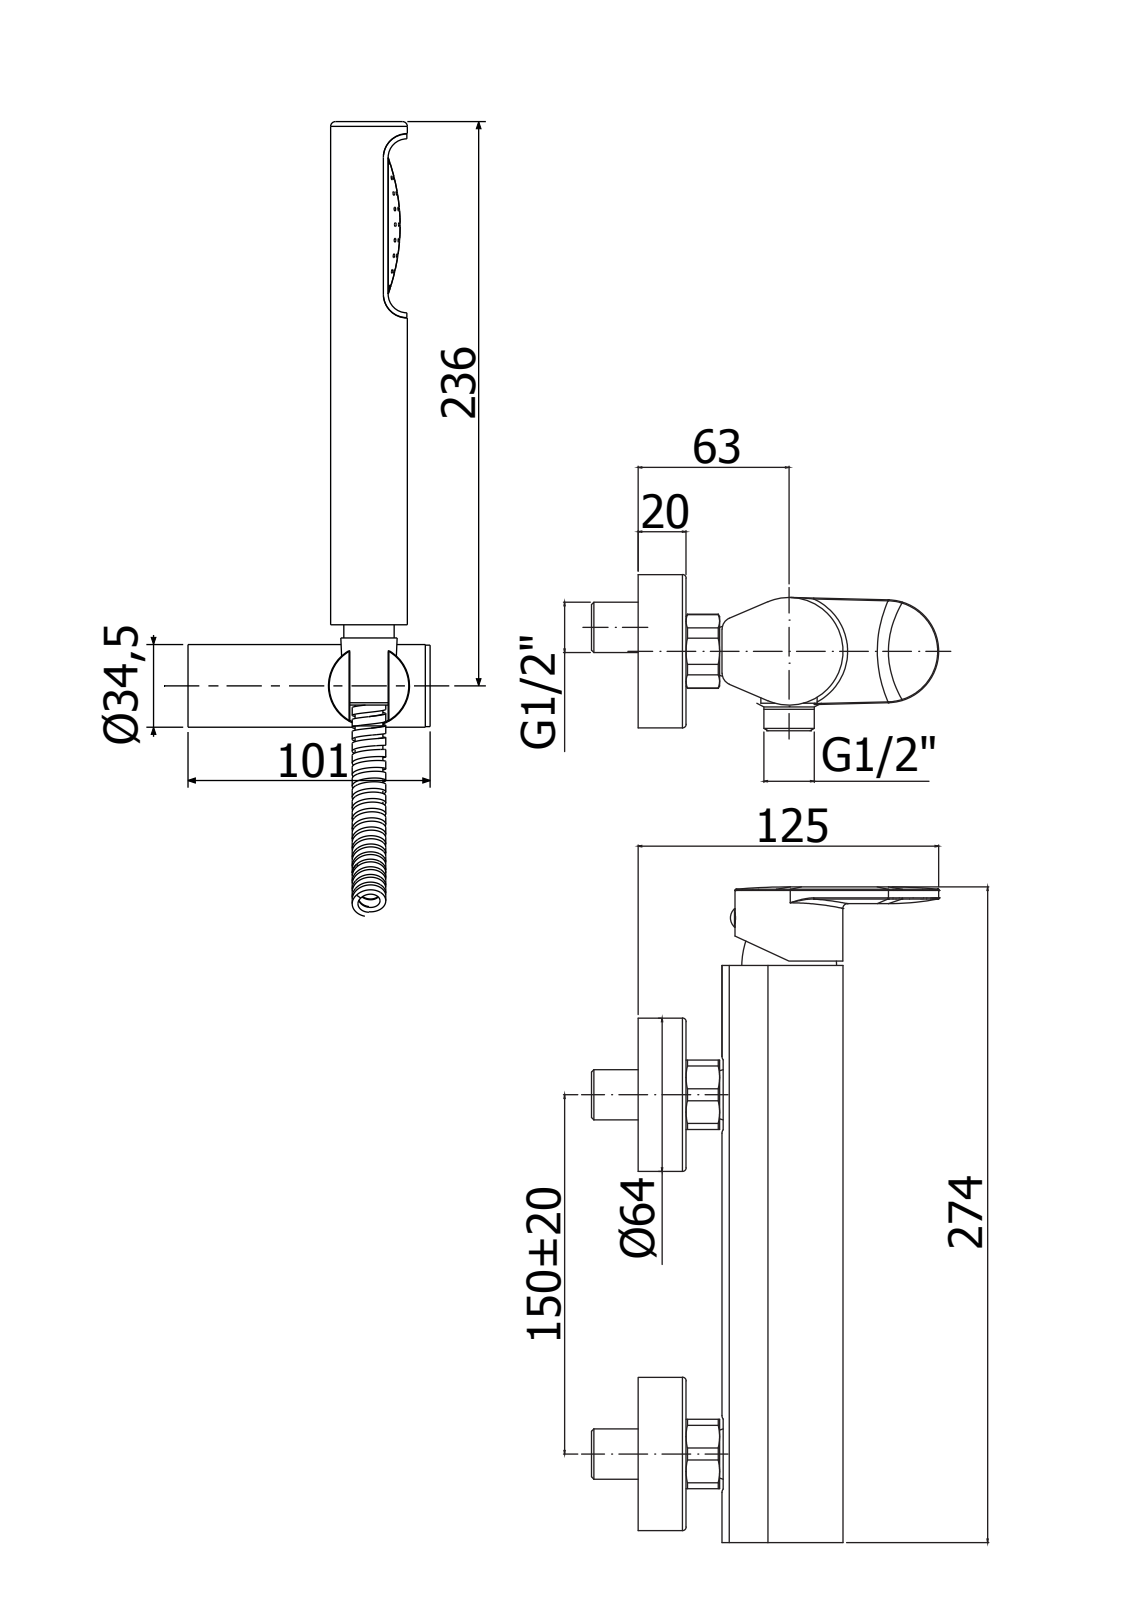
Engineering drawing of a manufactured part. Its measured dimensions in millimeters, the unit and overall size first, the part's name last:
Units: millimetres
Overall size (bounding box): 389.25 × 329.8 × 125.5
Round holes (diameter × count): ⌀3.5 ×2, ⌀10.5 ×2, ⌀3 ×1, ⌀4.5 ×1, ⌀7.8 ×1, ⌀15.1 ×1, ⌀16 ×1, ⌀19 ×1, ⌀20 ×1, ⌀23.8 ×1, ⌀28.5 ×1, ⌀30 ×1
Round bosses / shafts (diameter × count): ⌀63.5 ×2, ⌀17.7 ×2, ⌀45 ×1, ⌀34.5 ×1, ⌀34 ×1, ⌀33.8 ×1, ⌀33.5 ×1, ⌀32 ×1
Partial cylindrical surfaces — rounded edges, fillets, slot ends (radius × count): R1.5 ×44, R0.3 ×6, R3 ×4, R1.3 ×2, R5 ×2, R15.5 ×2, R18.5 ×2, R3.5 ×1
Main face-to-face distances: 3.7, 20, 49.2, 29.2, 35, 3.5, 15, 45.7, 25.7, 10.7
Hole centre spacings: 6, 6.5, 12.5, 73.6, 150, 223.6
Volume: 654 426 mm³ · Surface area: 180 927 mm²
Bodies: 3 solids, 612 faces (175 planar, 189 cylindrical, 248 other)
Part name (STEP PRODUCT): CA168DCR
STEP written by: CREO PARAMETRIC BY PTC INC, 2020044 (CONFIG_CONTROL_DESIGN)
